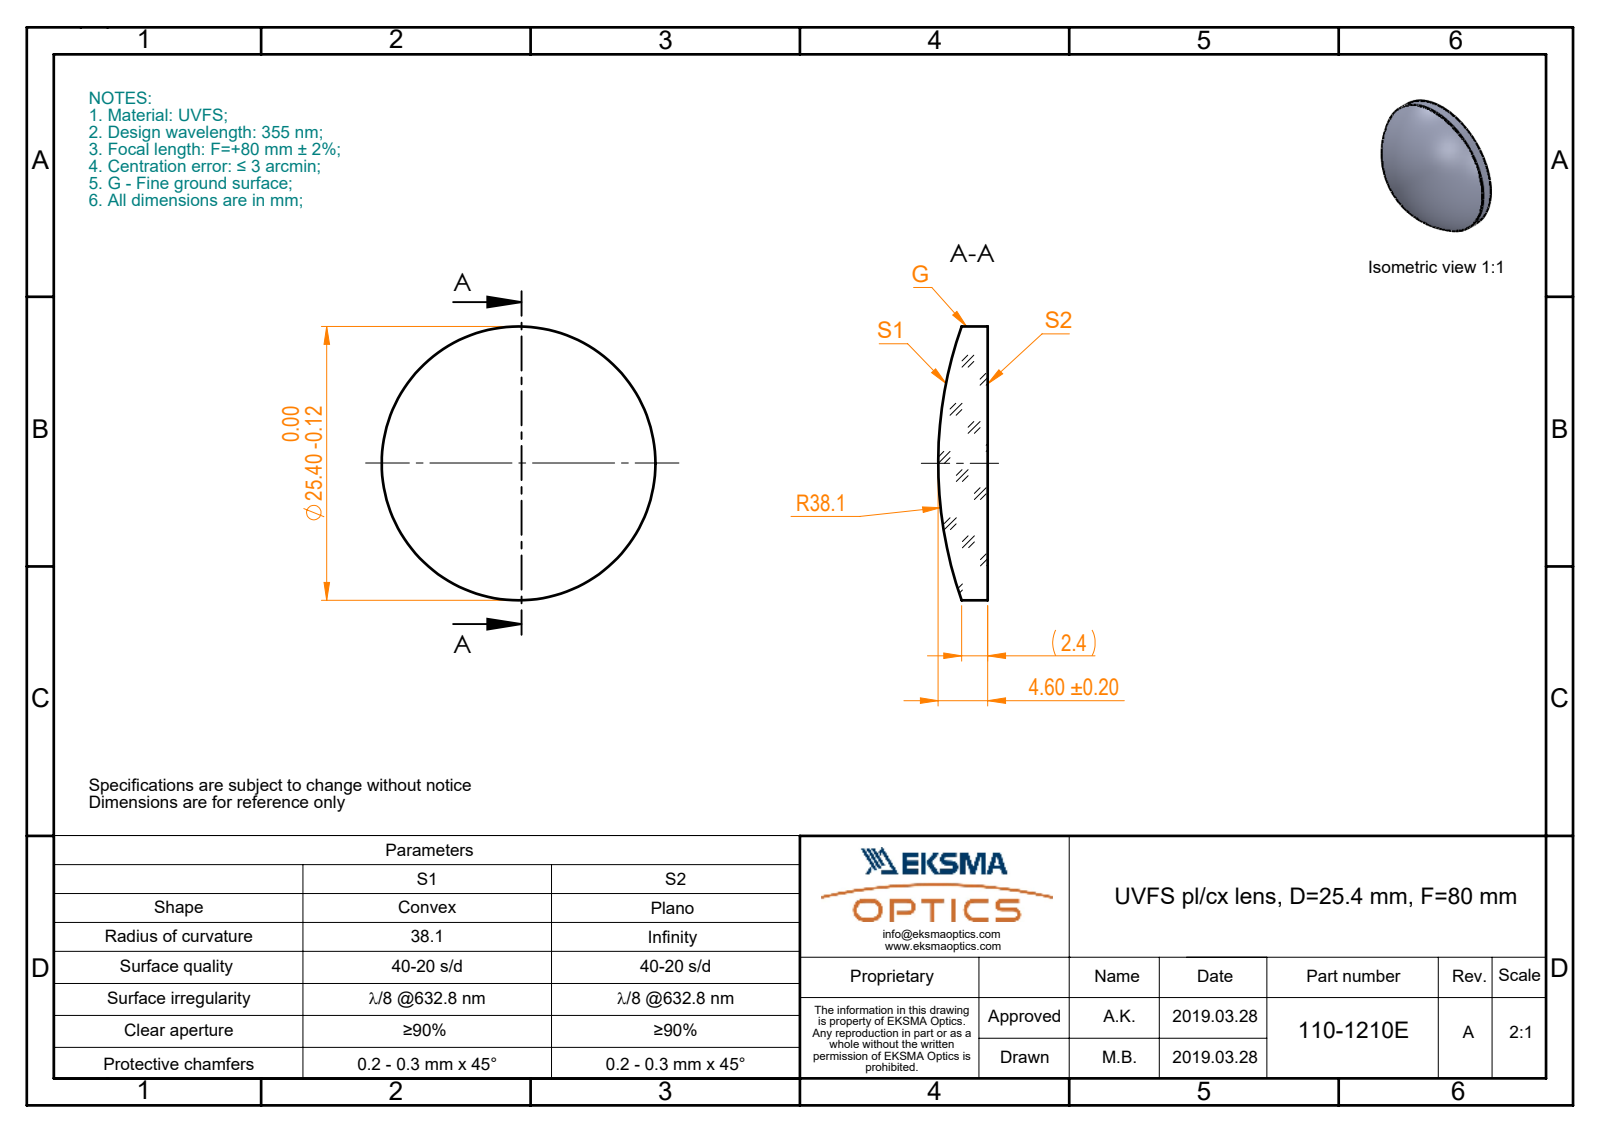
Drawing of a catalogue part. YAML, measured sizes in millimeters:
part_name: "110-1210E UVFS pl-cx 25.4 F80"
step_written_by: "SolidWorks 2017 (CONFIG_CONTROL_DESIGN)"
units: millimeters
bodies: {solids: 1, faces: 5, planar: 1, cylindrical: 2, other: 2}
overall_size: [25.4, 25.4, 4.6]
volume: 1784
surface_area: 1221
round_bosses_or_shafts:
  - {diameter: 25.4, count: 1}
